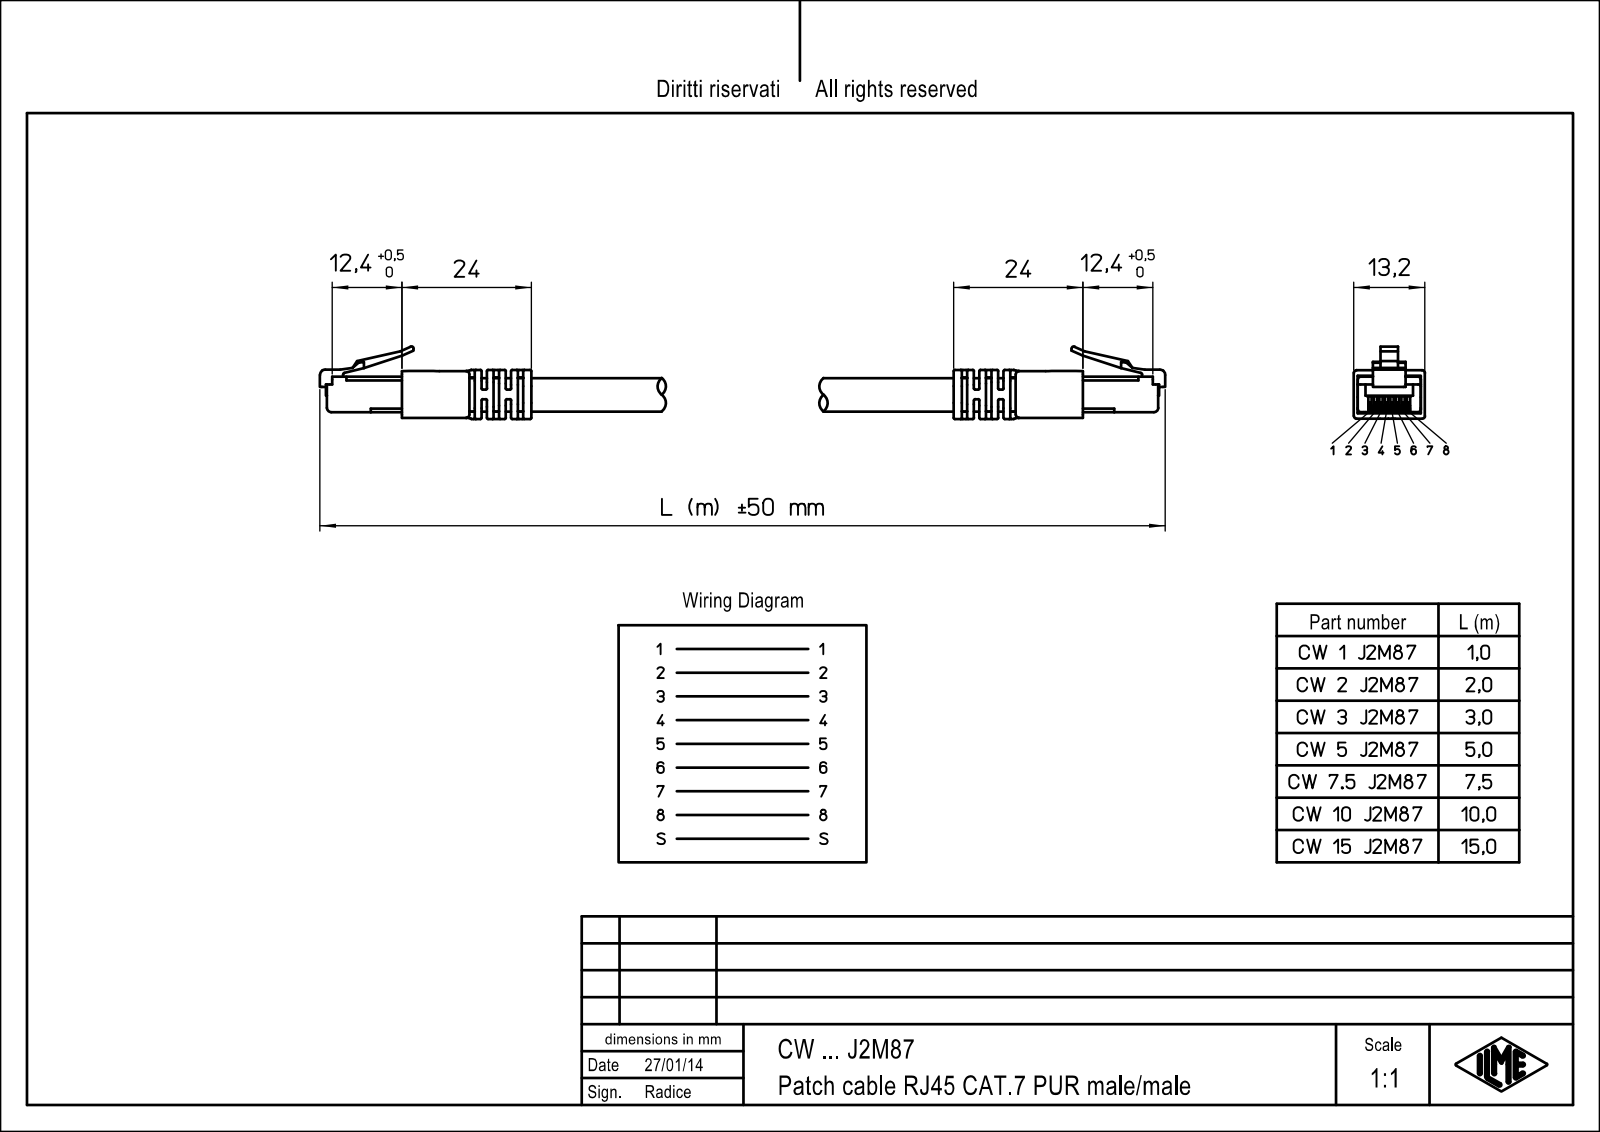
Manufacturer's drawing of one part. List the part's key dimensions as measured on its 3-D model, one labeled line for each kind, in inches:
Part name (STEP PRODUCT): CW_XXX_J2M87
STEP written by: Creo Elements/Direct Modeling 18.0B 02-Dec-2011 (C) Parametric Technology GmbH (AUTOMOTIVE_DESIGN)
Units: inches
Bodies: 1 solid, 1030 faces (372 planar, 450 cylindrical, 208 other)
Overall size (bounding box): 7.681 × 0.536 × 0.52
Volume: 0.552 in³ · Surface area: 11.92 in²
Round bosses / shafts (diameter × count): ⌀0.236 ×1
Partial cylindrical surfaces — rounded edges, fillets, slot ends (radius × count): R0.02 ×156, R0.008 ×10, R0.039 ×9, R0.011 ×8, R0.031 ×4, R0.015 ×2, R0.103 ×2
Main face-to-face distances: 0.301, 0.041, 0.039, 0.061, 0.079, 0.343, 0.118, 0.26, 0.02, 0.044
